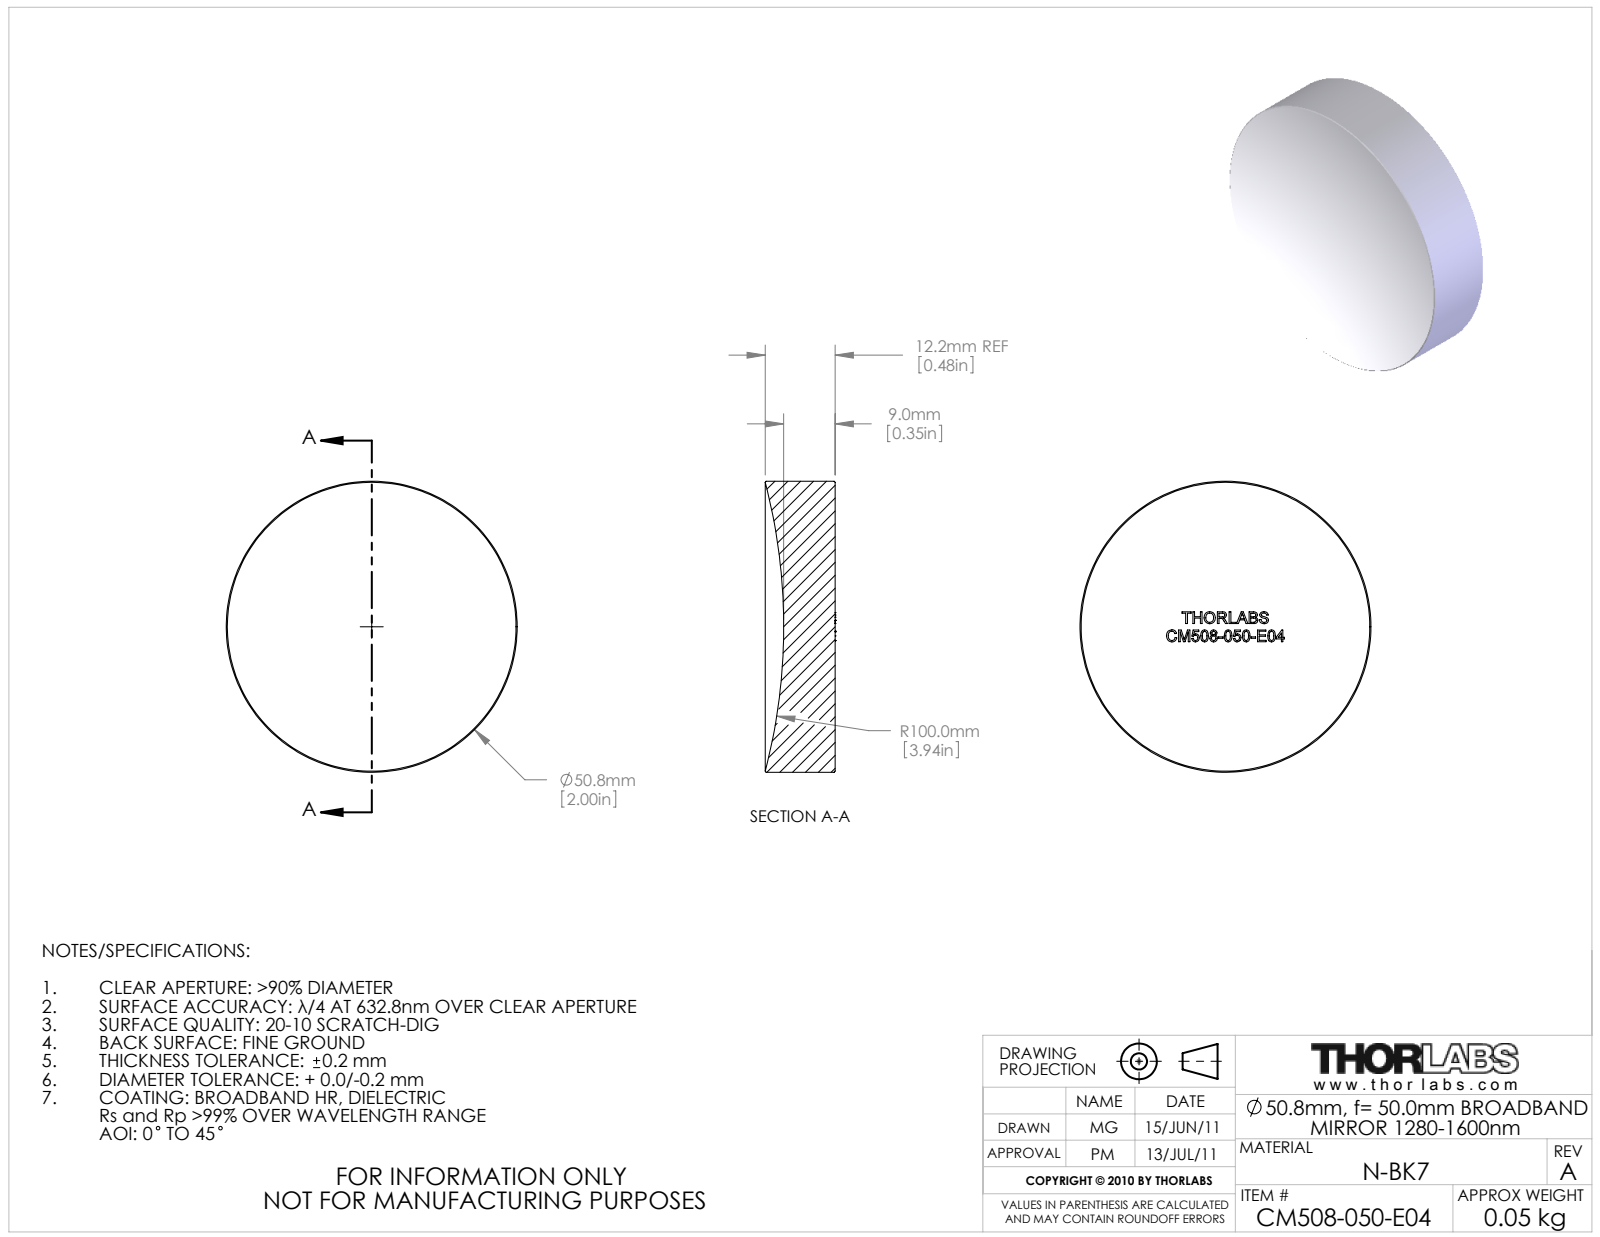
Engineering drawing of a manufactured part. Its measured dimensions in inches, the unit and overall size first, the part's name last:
Units: inches
Overall size (bounding box): 2 × 2 × 0.481
Round bosses / shafts (diameter × count): ⌀2 ×1
Main face-to-face distances: 0.081
Bodies: 0 solids, 44 faces (36 planar, 2 cylindrical, 6 other)
Part name (STEP PRODUCT): 22660-E0W
STEP written by: SolidWorks 2011 (AUTOMOTIVE_DESIGN)
